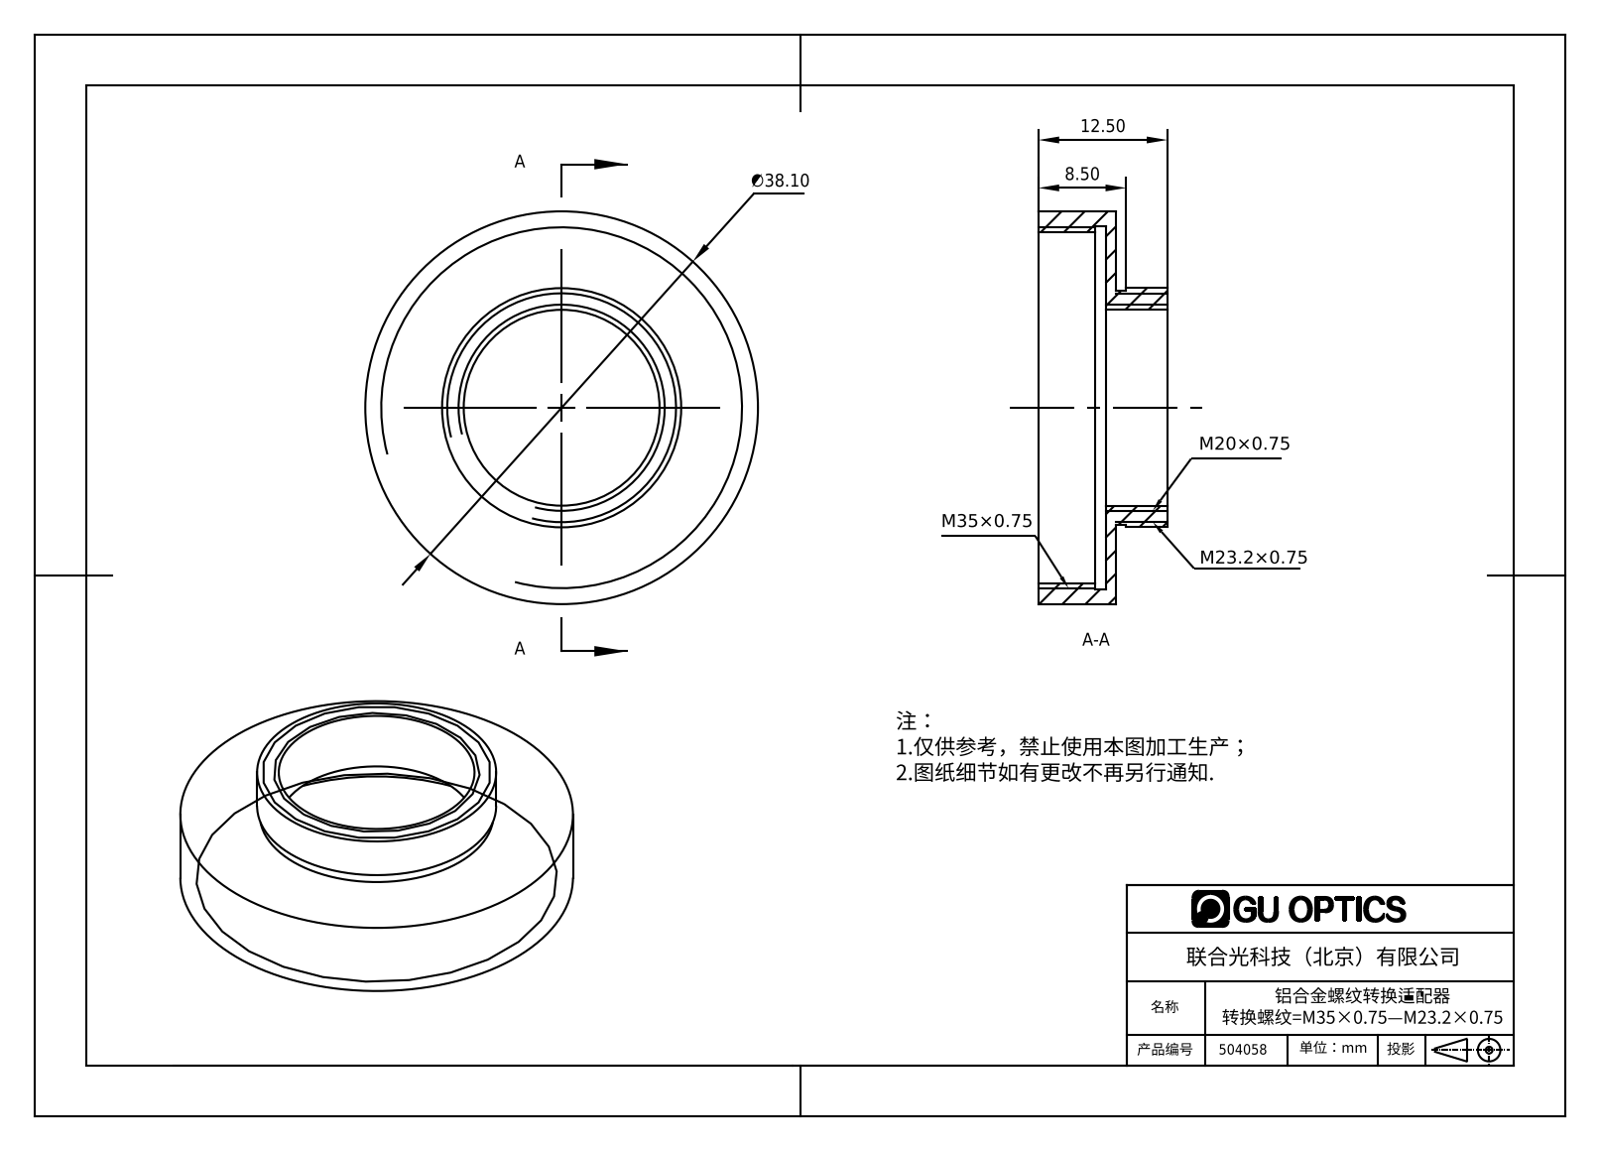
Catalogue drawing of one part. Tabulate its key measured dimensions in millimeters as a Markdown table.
| quantity | value |
| --- | --- |
| part name | 504058 |
| STEP written by | SolidWorks 2016 (AUTOMOTIVE_DESIGN) |
| units | millimeters |
| bodies | 1 solid, 18 faces (6 planar, 12 cylindrical, 0 other) |
| overall size | 38.1 × 38.1 × 12.5 |
| volume | 2 978 mm³ |
| surface area | 4 196 mm² |
| round holes (diameter × count) | 19 × 1, 34 × 1, 35.2 × 1 |
| round bosses / shafts (diameter × count) | 38.1 × 1, 23.2 × 1, 22.7 × 1 |
| main face-to-face distances | 1, 6.5, 7.5, 12.5, 6, 5, 2, 5.5, 7, 8.5 |
